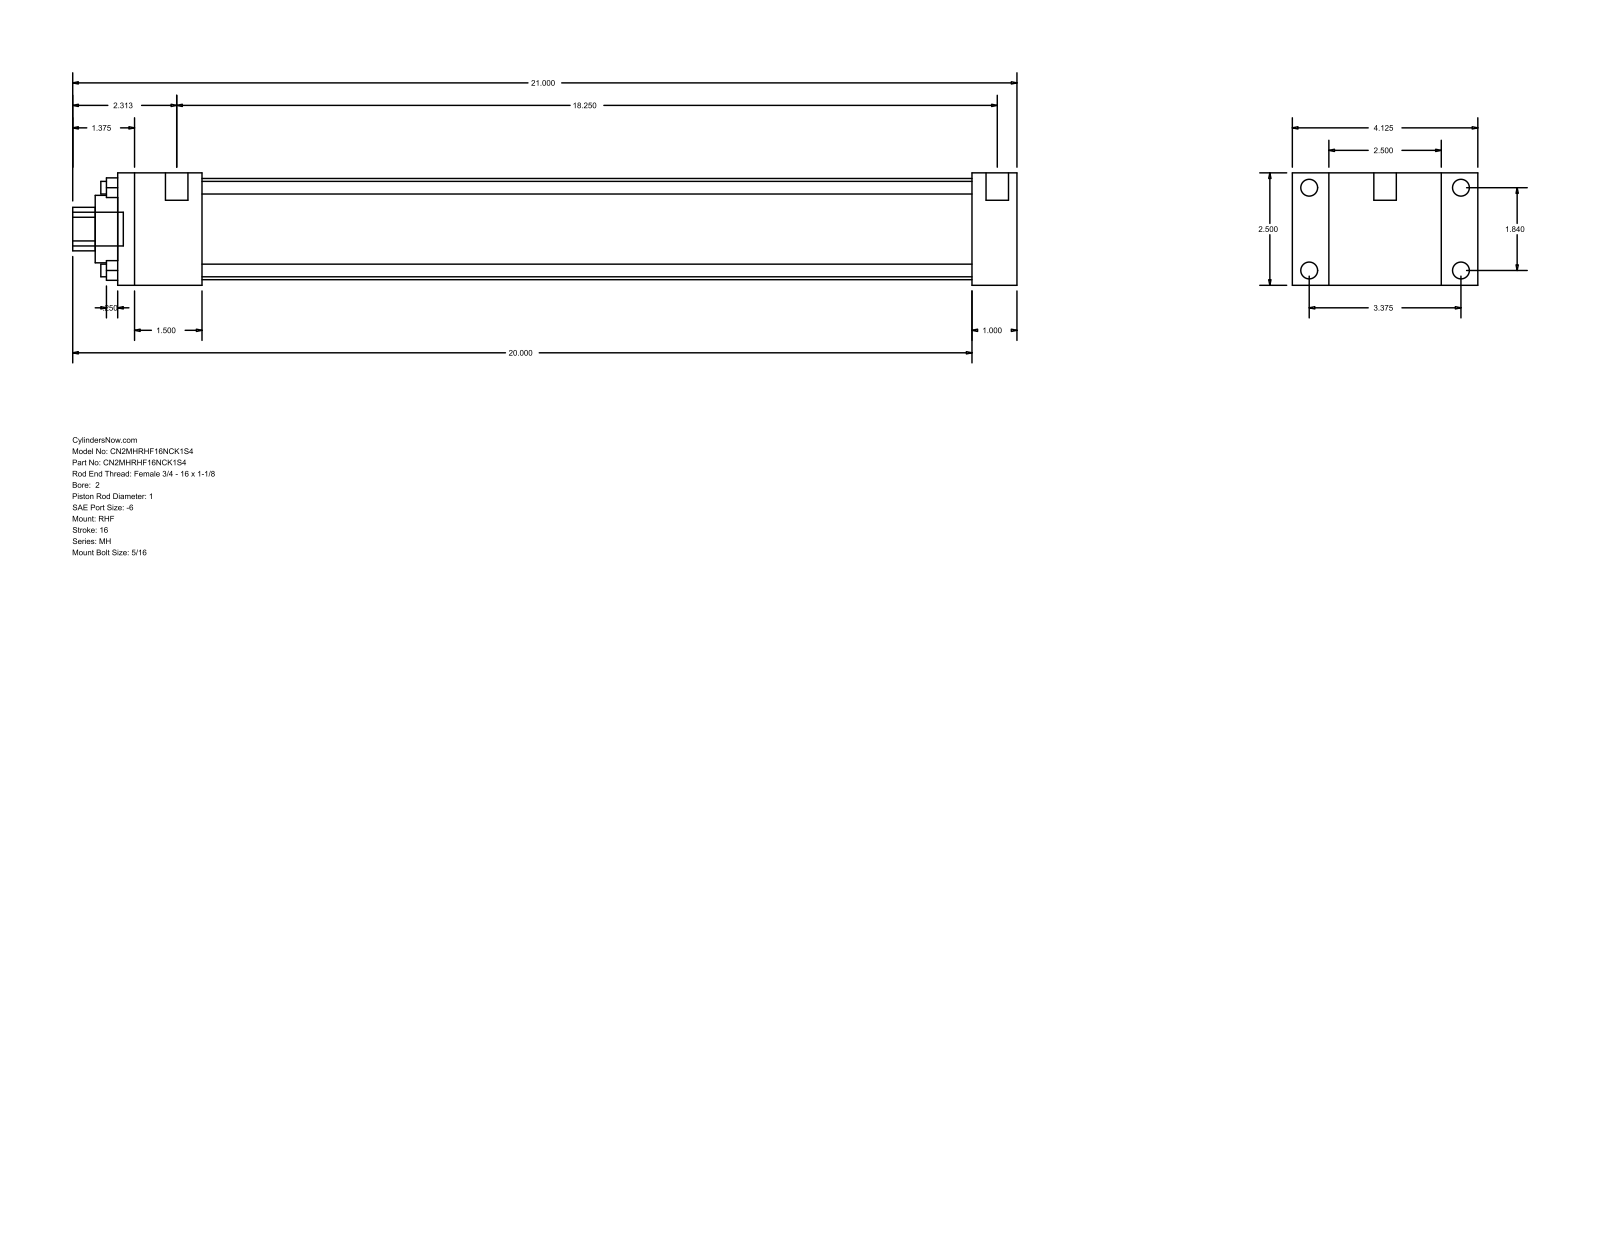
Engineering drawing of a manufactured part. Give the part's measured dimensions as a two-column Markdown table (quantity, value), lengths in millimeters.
| quantity | value |
| --- | --- |
| part name | MH_RHF__0200_1 |
| STEP written by | GSSL Pune (CONFIG_CONTROL_DESIGN) |
| units | millimeters |
| bodies | 0 solids, 88 faces (60 planar, 28 cylindrical, 0 other) |
| overall size | 533.4 × 104.78 × 63.5 |
| round holes (diameter × count) | 7.14 × 4, 25.4 × 1, 38.1 × 1, 57.15 × 1 |
| round bosses / shafts (diameter × count) | 9.53 × 4, 5.56 × 4, 12.7 × 2, 19.05 × 1 |
| partial cylindrical surfaces (radius × count) | 12.29 × 1 |
| main face-to-face distances | 63.5, 25.4, 20.64, 84.14, 508, 482.6, 104.78, 47.63, 434.97, 460.37 |
| hole center spacings | 33.05, 46.74, 66.1 |
